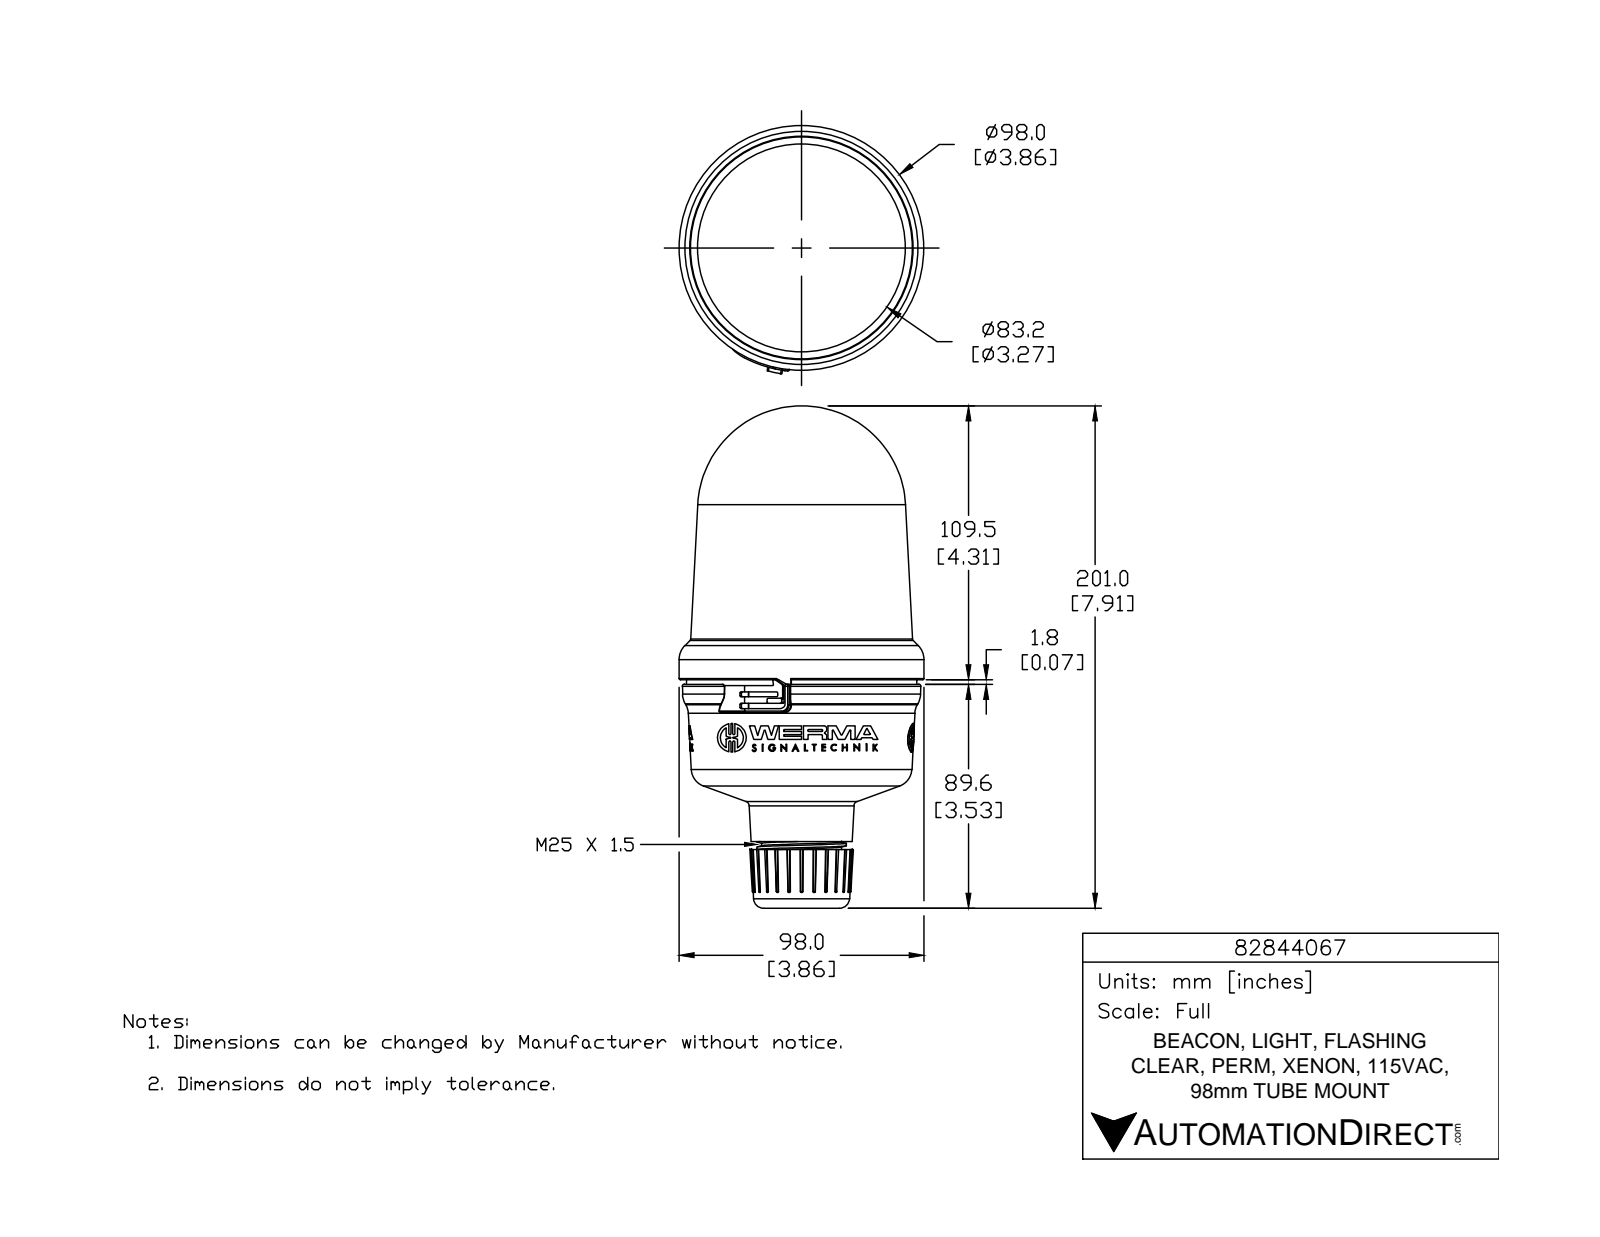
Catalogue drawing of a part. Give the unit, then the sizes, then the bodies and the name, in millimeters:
Units: millimetres
Overall size (bounding box): 201 × 99.4 × 98
Round holes (diameter × count): ⌀2 ×3, ⌀25.7 ×1, ⌀26 ×1
Round bosses / shafts (diameter × count): ⌀11.5 ×3, ⌀2.9 ×3, ⌀98 ×1, ⌀35.8 ×1, ⌀32 ×1
Partial cylindrical surfaces — rounded edges, fillets, slot ends (radius × count): R0.5 ×12, R0.2 ×9, R0.2 ×6, R0.4 ×6, R0.4 ×6, R0.4 ×6, R6.7 ×6, R0.2 ×3
Main face-to-face distances: 56.2, 11.7, 68, 8.5, 3.2, 64.7, 66.1, 62.9, 54.4, 1.9
Volume: 896 400 mm³ · Surface area: 58 960 mm²
Bodies: 1 solid, 1006 faces (554 planar, 189 cylindrical, 263 other)
Part name (STEP PRODUCT): 82844067
STEP written by: SolidWorks 2015 (AUTOMOTIVE_DESIGN)
